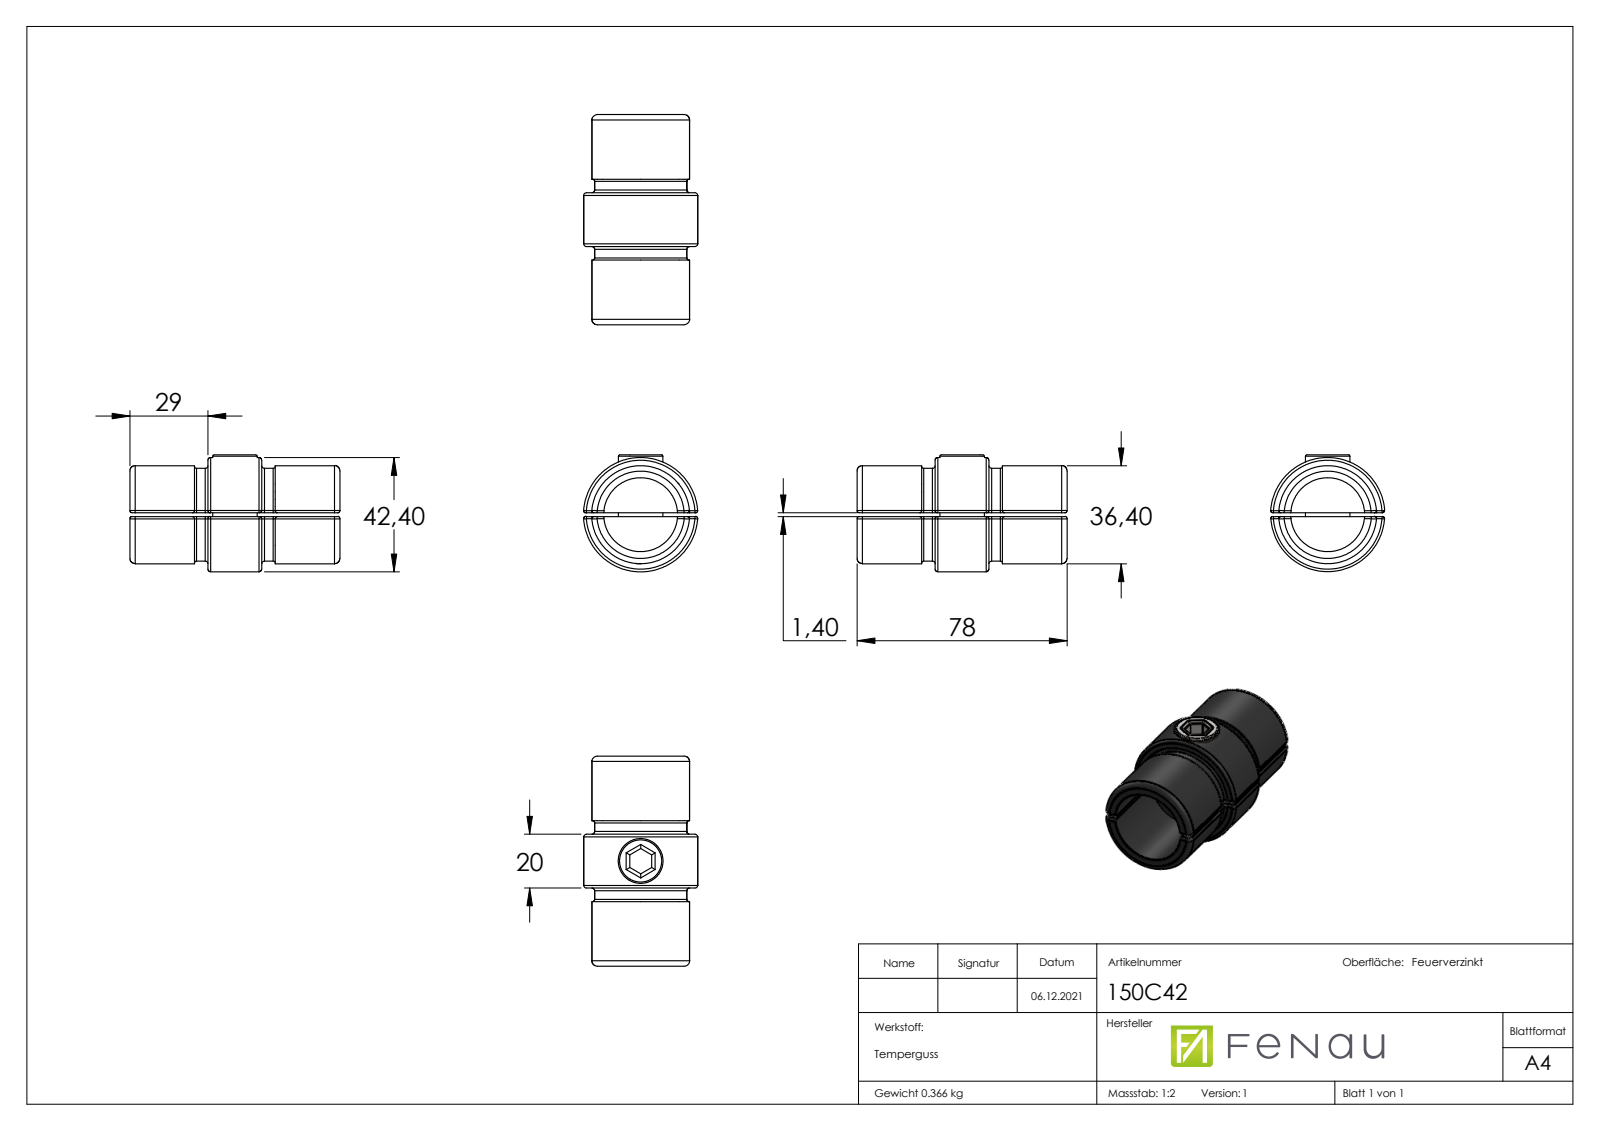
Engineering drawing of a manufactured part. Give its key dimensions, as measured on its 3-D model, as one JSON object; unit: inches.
{"part_name": "150-C42 Teil3; 150-C42 Teil1; 150-C42 Teil2; 150-C42", "step_written_by": "SolidWorks 2018 (CONFIG_CONTROL_DESIGN)", "units": "inches", "bodies": {"solids": 3, "faces": 265, "planar": 54, "cylindrical": 122, "other": 89}, "overall_size": [3.071, 1.709, 1.665], "volume_in3": 3.043, "surface_area_in2": 34.7, "round_holes": [[0.6, 1], [1.079, 1]], "round_bosses_or_shafts": [[1.669, 1], [1.433, 1], [0.65, 1]], "partial_cylinders_radius": [[0.079, 32], [0.031, 24], [0.02, 12]], "face_to_face_distances": [0.055, 0.787, 1.142, 1.929, 0.319, 3.071, 0.965, 0.902, 0.846, 0.063]}
